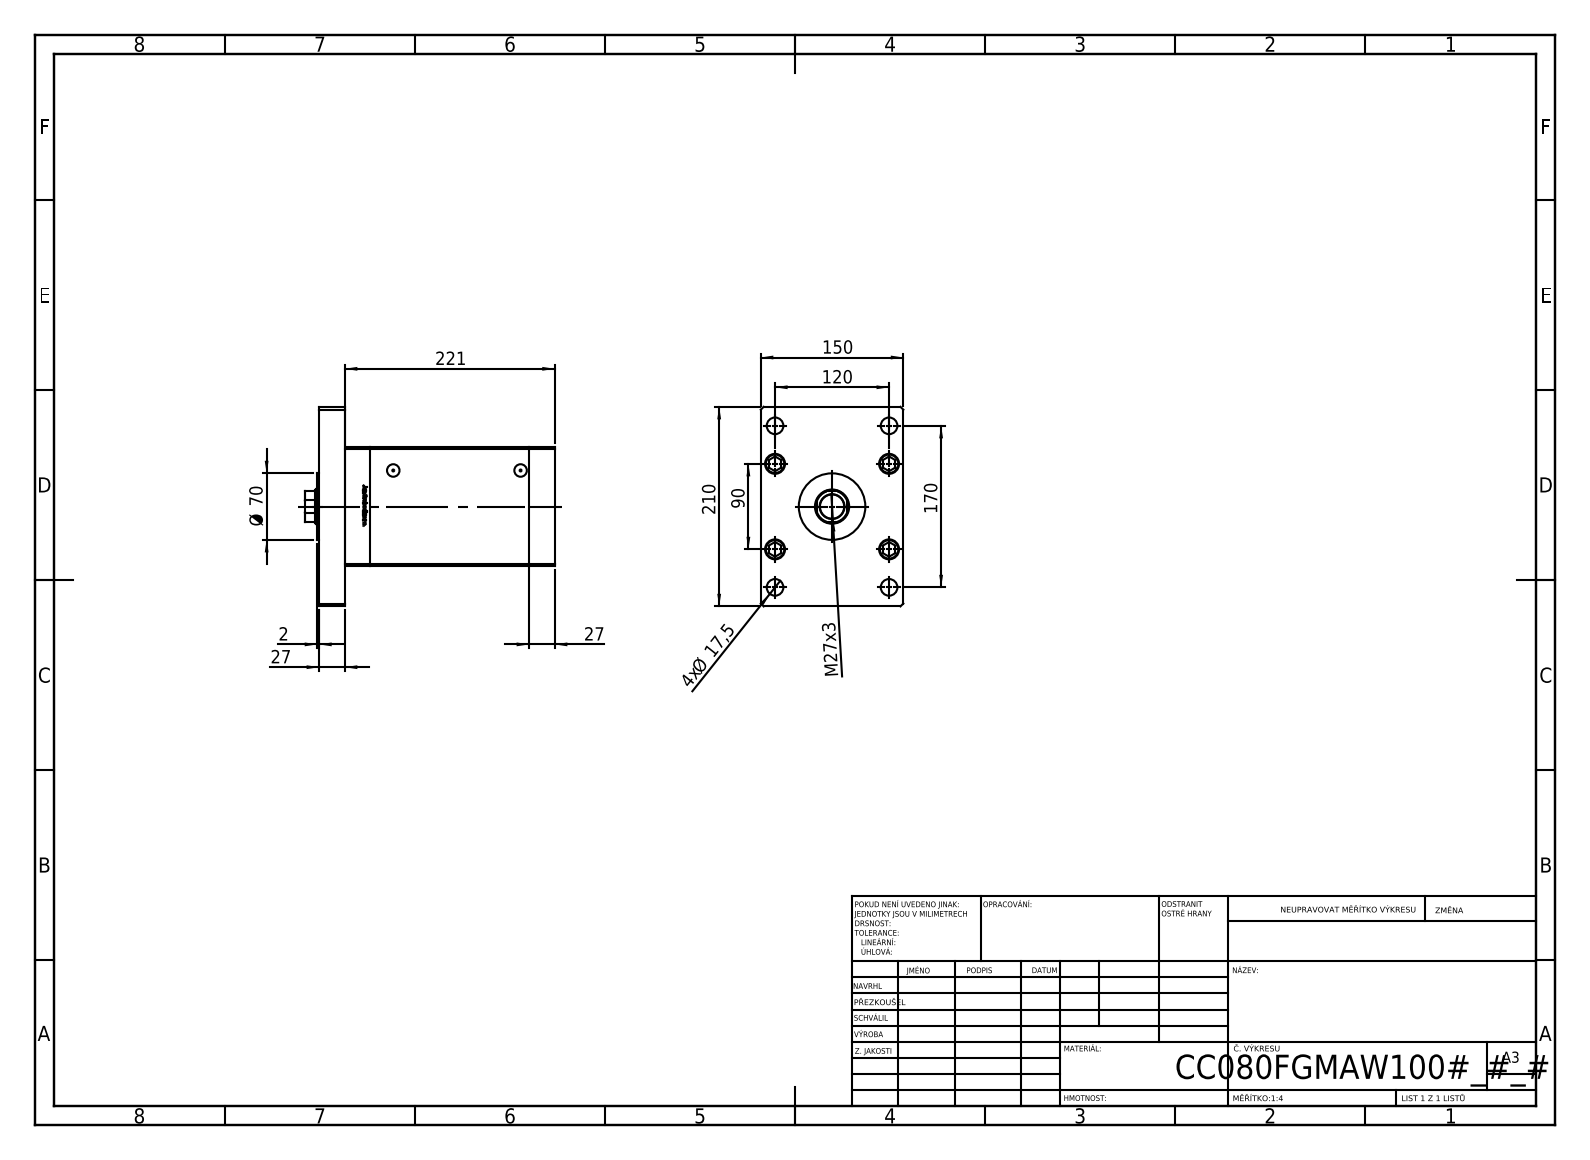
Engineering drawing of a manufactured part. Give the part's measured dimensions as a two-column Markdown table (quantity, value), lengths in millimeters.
| quantity | value |
| --- | --- |
| part name | V220C_VC_F; V220C_F; V220C BACK_F; V220C_F_MIDDLE (+2 more) |
| STEP written by | SolidWorks 2019 (CONFIG_CONTROL_DESIGN) |
| units | millimeters |
| bodies | 19 solids, 1309 faces (516 planar, 187 cylindrical, 606 other) |
| overall size | 263 × 210 × 150 |
| volume | 4 363 000 mm³ |
| surface area | 472 173 mm² |
| round holes (diameter × count) | 17.5 × 9, 22 × 5, 16 × 4, 21 × 4, 2 × 2, 13.16 × 2, 25.5 × 1, 36 × 1, 37.5 × 1 |
| round bosses / shafts (diameter × count) | 8 × 9, 21 × 5, 80 × 1, 70 × 1 |
| partial cylindrical surfaces (radius × count) | 0.93 × 2, 17.5 × 1 |
| main face-to-face distances | 27, 194, 221, 150, 125, 167, 54, 248, 33.5, 6.5 |
| hole center spacings | 51, 40, 75, 104.04, 120, 126.49, 130, 176.92 |
